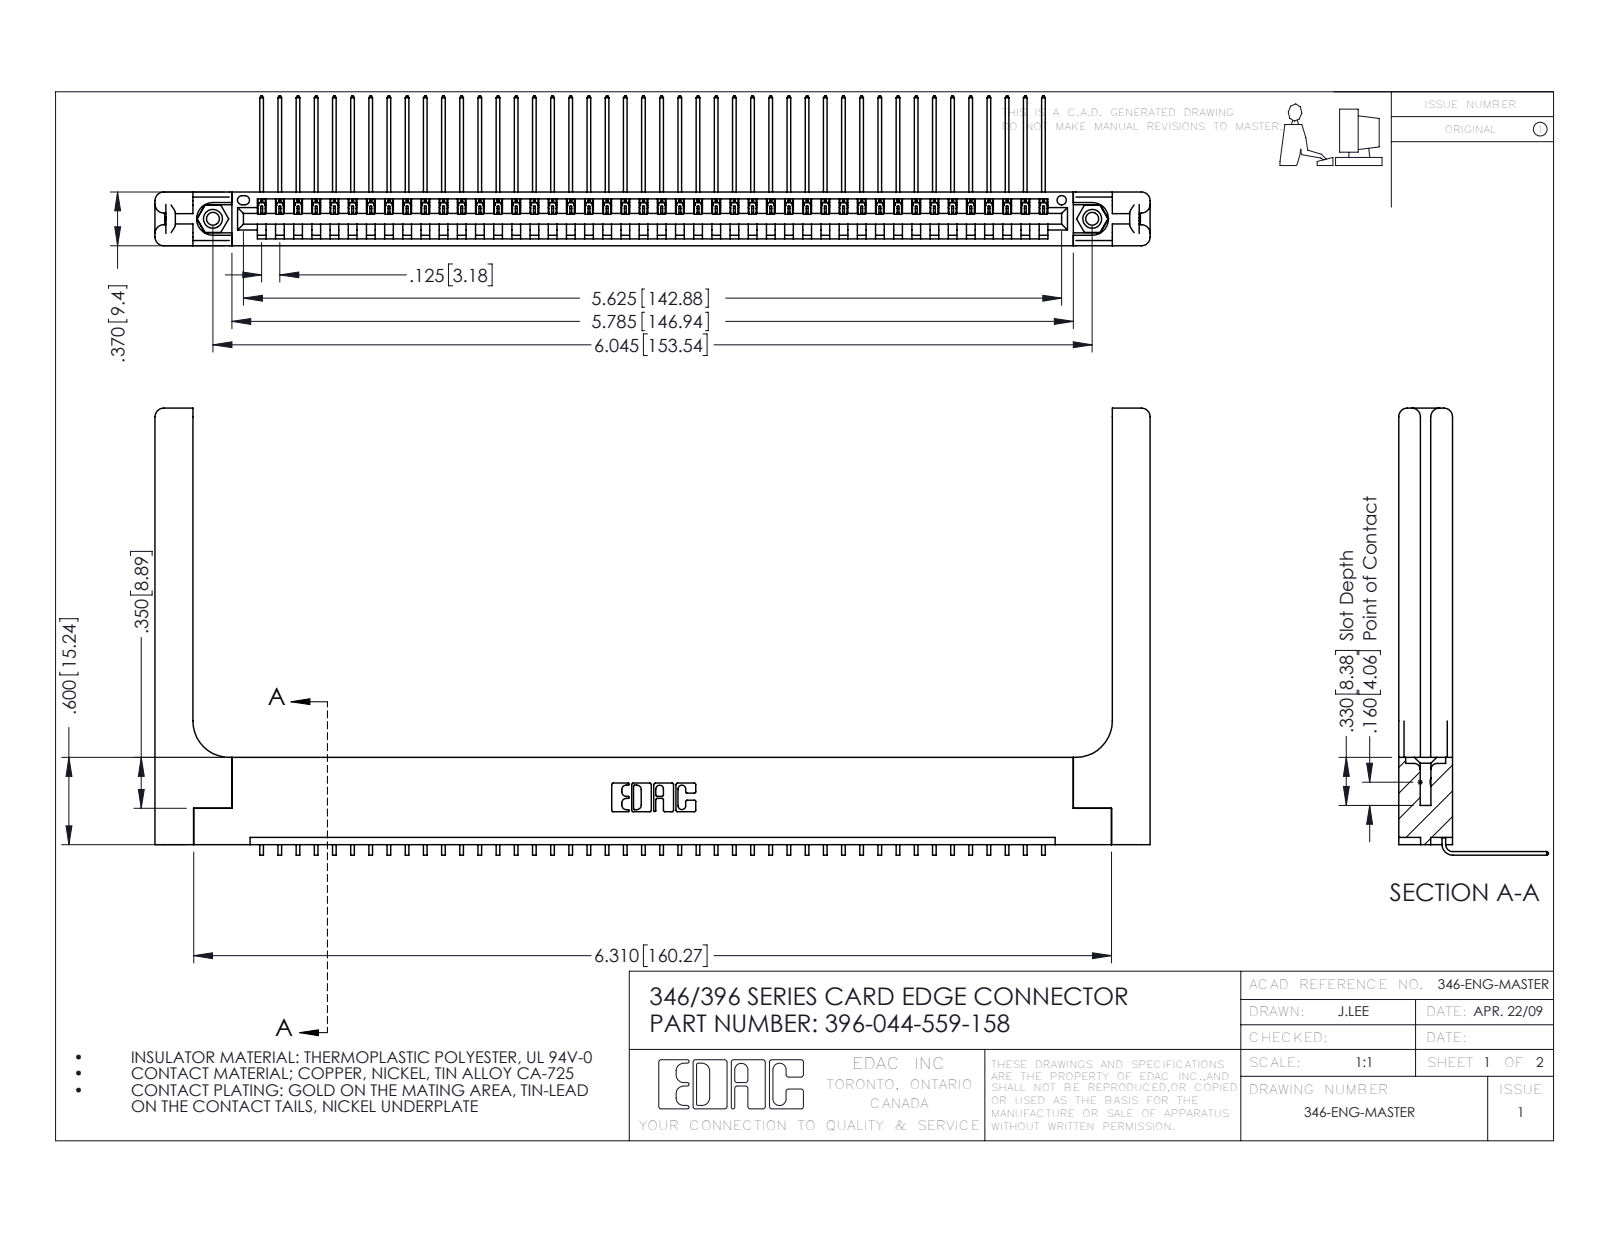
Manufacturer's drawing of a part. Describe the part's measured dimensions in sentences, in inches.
The part is named "396-044-559-158; 345-250-001_345-250-001-102; 346-220-058_345-220-058; 346 Part_Flush Mounting Lugs - 0.156 Dia-TH (+1 more)". Its 3-D file was written by "SolidWorks 2016 (CONFIG_CONTROL_DESIGN)". It is 49 solids with 3018 faces: 2072 planar, 886 cylindrical and 60 other. Overall it measures 6.841 by 3.073 by 1.03 inches. Its volume is 1.484 cubic inches and its surface area 41.94 square inches. Round holes: 2 of diameter 0.089, 2 of diameter 0.125, 2 of diameter 0.156, 1 of diameter 0.064. Round bosses or shafts: 2 of diameter 0.155. Partial cylindrical surfaces (rounded edges, fillets, slot ends): 88 of radius 0.006, 22 of radius 0.01, 16 of radius 0.06, 6 of radius 0.007, 6 of radius 0.031, 3 of radius 0.026, 2 of radius 0.03, 2 of radius 0.031. The main face-to-face distances are 0.37, 0.048, 0.322, 0.072, 0.148, 0.15, 0.025, 0.25, 0.298, 0.222. The hole center spacings are 0.246, 5.836, 6.045.
